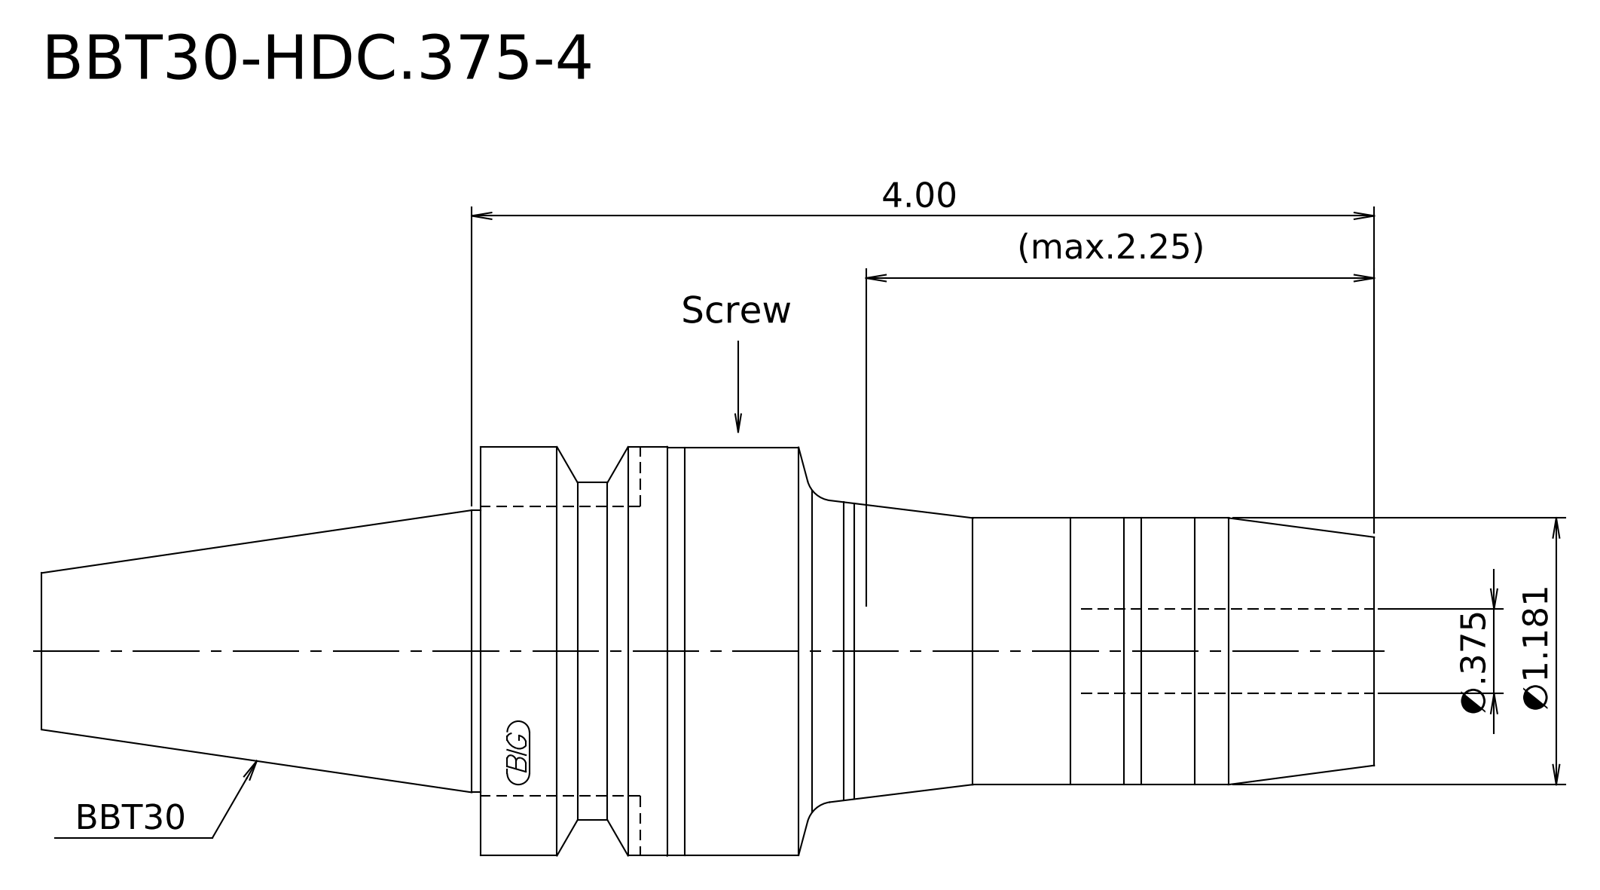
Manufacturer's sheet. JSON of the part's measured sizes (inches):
{"step_written_by": "Kubotek KeyCreator 2011 V10.0.2 (22737) (automotive_design)", "units": "inches", "bodies": {"solids": 1, "faces": 16, "planar": 3, "cylindrical": 6, "other": 7}, "overall_size": [5.906, 1.811, 1.811], "volume_in3": 7.853, "surface_area_in2": 27.63, "round_bosses_or_shafts": [[1.811, 1], [1.807, 1], [1.496, 1], [1.25, 1], [1.181, 1]], "face_to_face_distances": [3.961, 5.906, 1.945]}
